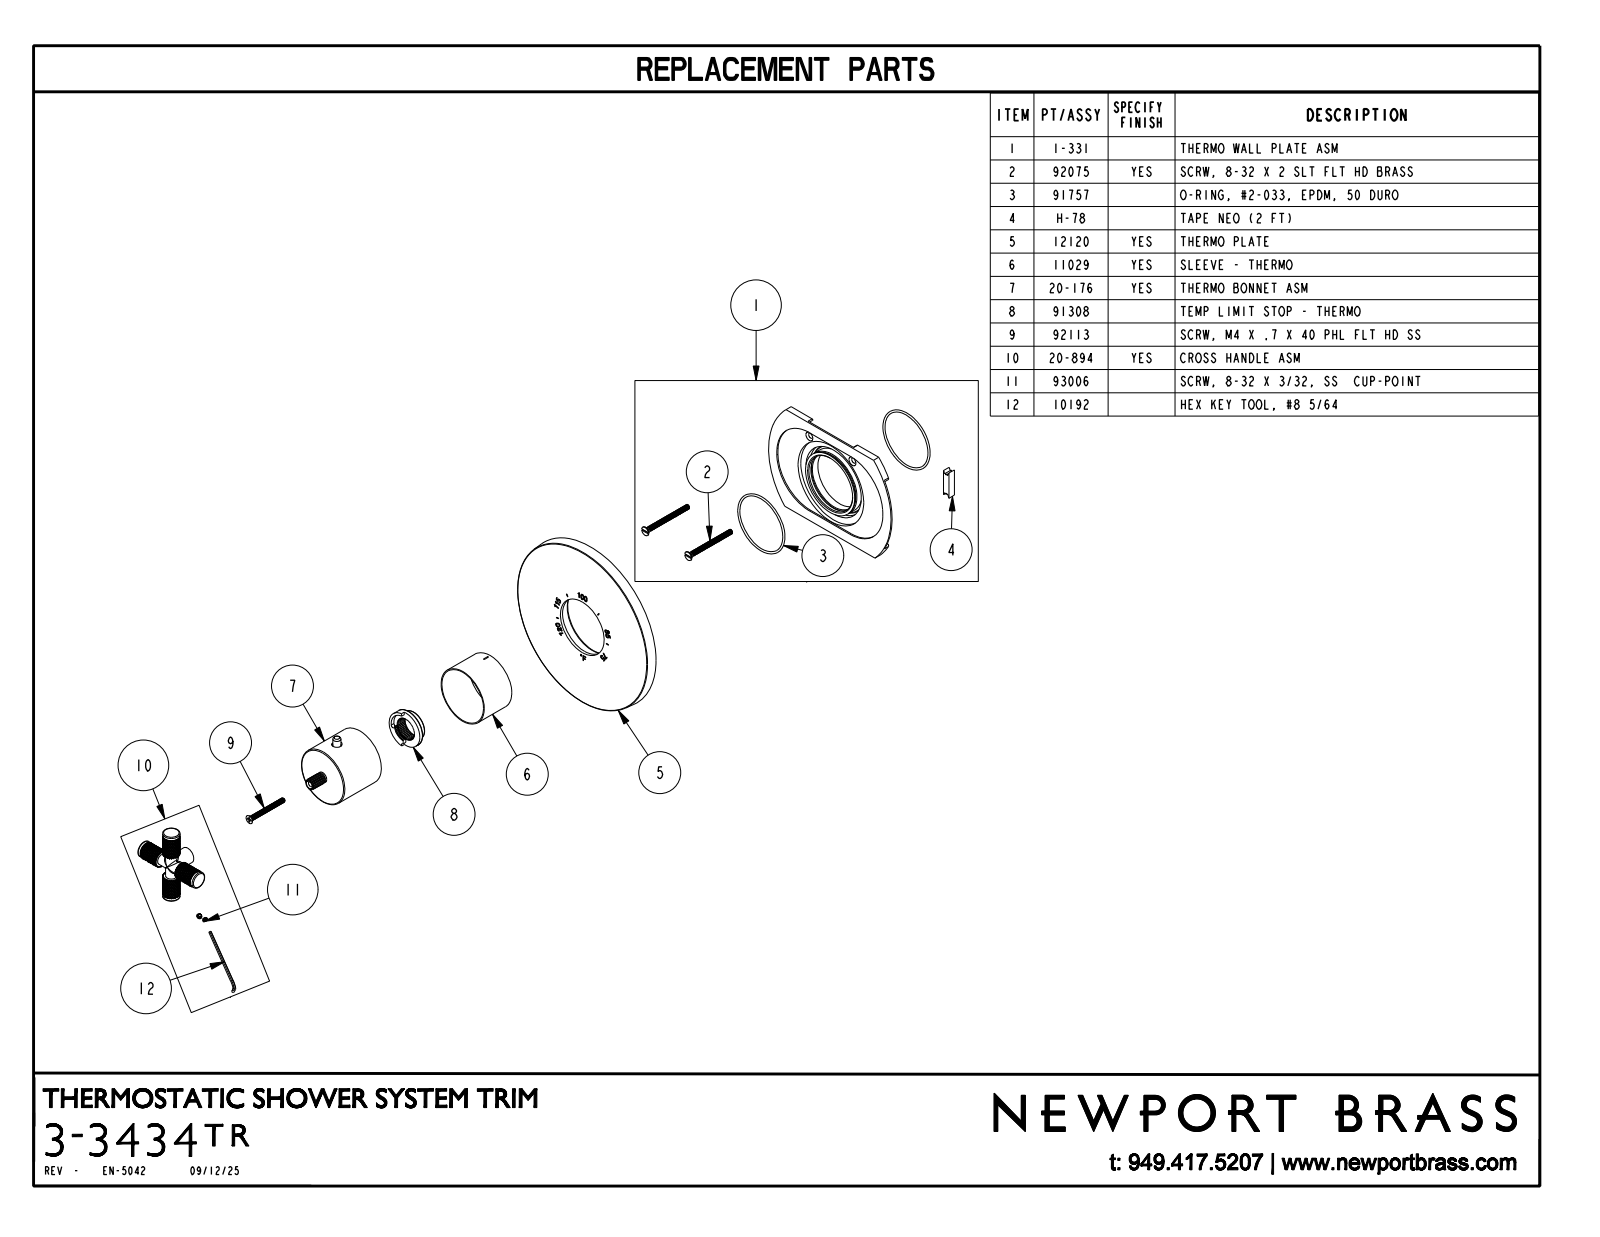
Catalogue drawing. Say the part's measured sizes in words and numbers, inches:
The part is named "3-3434TR". Its 3-D file was written by "CREO PARAMETRIC BY PTC INC, 2025093 (CONFIG_CONTROL_DESIGN)". It is 1 solid with 7842 faces: 120 planar, 1430 cylindrical and 6292 other. Overall it measures 6 by 5.994 by 3.713 inches. Its volume is 18.61 cubic inches and its surface area 89.02 square inches. Round holes: 1 of diameter 2. Round bosses or shafts: 2 of diameter 0.563, 2 of diameter 0.562, 2 of diameter 0.375, 1 of diameter 1.97, 1 of diameter 0.55, 1 of diameter 0.26. Partial cylindrical surfaces (rounded edges, fillets, slot ends): 1 of radius 0.955, 1 of radius 2.91. The main face-to-face distances are 0.375, 2.679, 2.304, 0.825, 1.701, 2.526, 0.876, 0.362, 0.013, 2.317.
